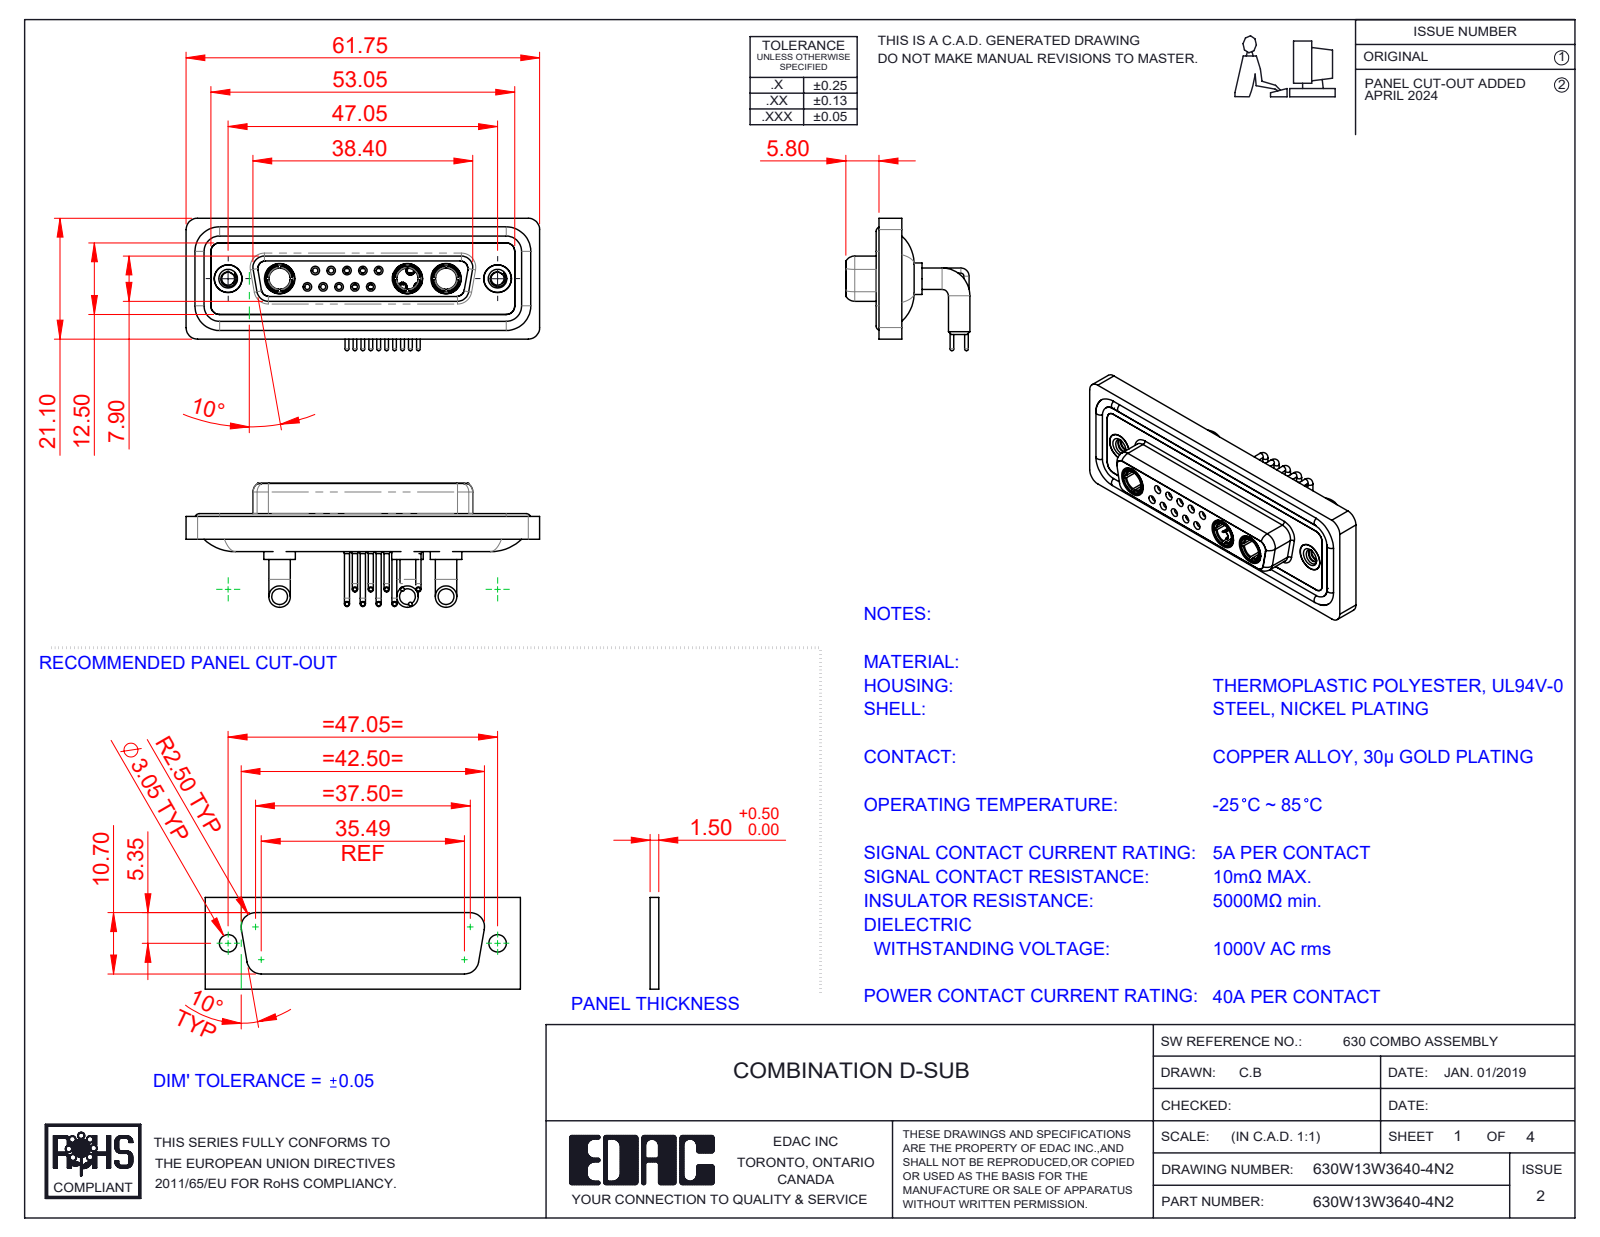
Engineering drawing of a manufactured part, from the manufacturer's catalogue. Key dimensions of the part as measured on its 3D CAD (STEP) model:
Part name (STEP PRODUCT): 630Combo Threaded Rivet_2; 630Combo Housing_13W3; 630Combo Contact Row 2_50 Contacts; Power Socket_40A RA (+5 more)
STEP written by: SolidWorks 2023 (CONFIG_CONTROL_DESIGN)
Units: millimetres
Bodies: 23 solids, 1150 faces (342 planar, 493 cylindrical, 315 other)
Overall size (bounding box): 61.75 × 23.12 × 21.68
Volume: 8 688 mm³ · Surface area: 14 428 mm²
Round holes (diameter × count): ⌀0.9 ×10, ⌀1.1 ×10, ⌀1.5 ×10, ⌀2 ×10, ⌀1.6 ×5, ⌀1.7 ×5, ⌀4.85 ×5, ⌀3.7 ×3, ⌀5.3 ×3, ⌀2.26 ×2, ⌀4 ×2, ⌀4.05 ×2
Round bosses / shafts (diameter × count): ⌀0.9 ×15, ⌀1.6 ×12, ⌀0.65 ×10, ⌀3.75 ×6, ⌀2 ×5, ⌀1.5 ×5, ⌀5.5 ×3, ⌀5.2 ×3
Partial cylindrical surfaces — rounded edges, fillets, slot ends (radius × count): R1.5 ×18, R2 ×18, R1.35 ×8, R1.6 ×8, R0.25 ×4, R0.5 ×4, R0.6 ×4, R0.65 ×4
Main face-to-face distances: 0.4, 1.8, 4.1, 1.1, 1.6, 3.1, 2.5, 1.5, 3.7, 1.4
Hole centre spacings: 3.16, 2.77, 5.54, 5.04, 8.31, 5.03, 7.49, 11.08
